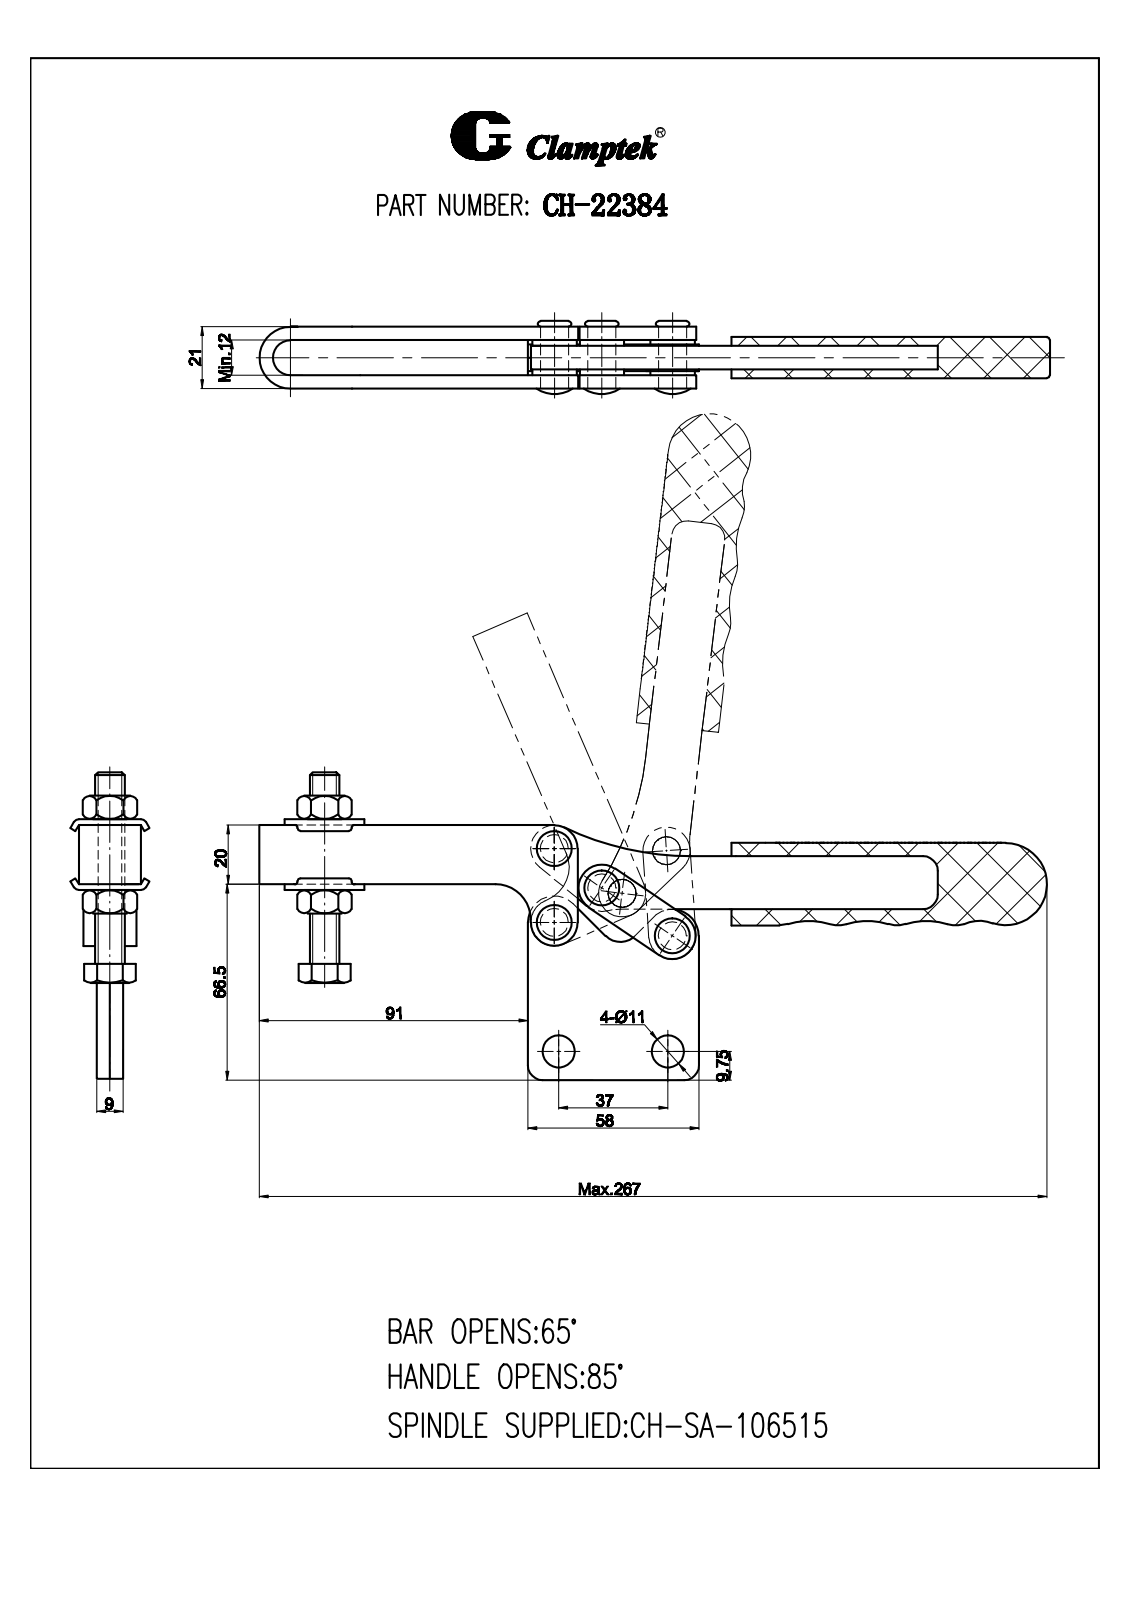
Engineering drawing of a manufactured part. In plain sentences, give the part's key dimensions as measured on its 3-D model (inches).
The part is named "22384-02; FW120; 106512; CH-22384 (+7 more)". Its 3-D file was written by "SolidWorks 2012 (CONFIG_CONTROL_DESIGN)". It is 24 solids with 1053 faces: 357 planar, 372 cylindrical and 324 other. Overall it measures 10.692 by 4.07 by 1.284 inches. Its volume is 7.517 cubic inches and its surface area 108.1 square inches. Round holes: 4 of diameter 0.374, 4 of diameter 0.394, 2 of diameter 0.331, 2 of diameter 0.433, 2 of diameter 0.512, 1 of diameter 0.205. Round bosses or shafts: 4 of diameter 0.63, 4 of diameter 0.472, 4 of diameter 0.354, 1 of diameter 0.394, 1 of diameter 0.142. Partial cylindrical surfaces (rounded edges, fillets, slot ends): 84 of radius 0.01, 8 of radius 1.02, 7 of radius 0.138, 5 of radius 0.197, 4 of radius 0.118, 4 of radius 0.394, 2 of radius 0.354, 2 of radius 0.61. The main face-to-face distances are 0.236, 0.177, 0.413, 0.157, 0.079, 0.335, 0.394, 0.059, 0.02, 0.118. The hole center spacings are 0.791, 0.821, 0.984, 1.138, 1.457, 1.558, 1.585, 1.735.
